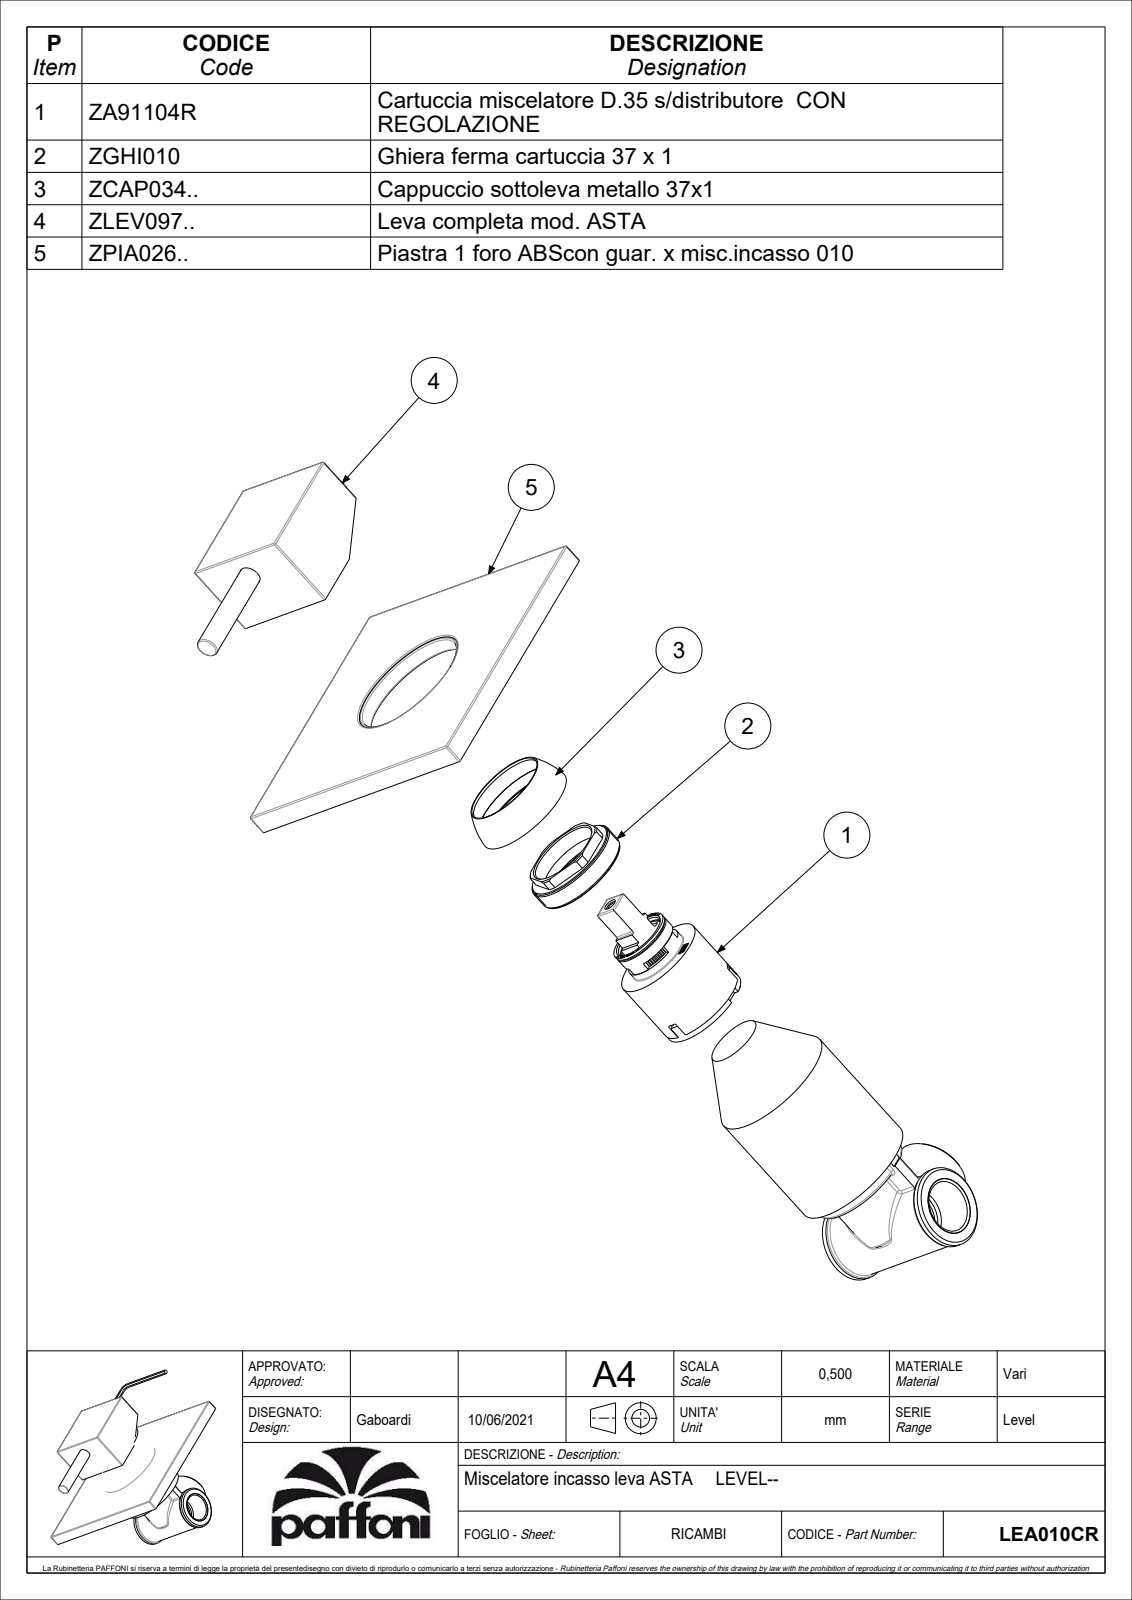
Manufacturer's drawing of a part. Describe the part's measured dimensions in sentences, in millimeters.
The part is named "LEA010CR". Its 3-D file was written by "CREO PARAMETRIC BY PTC INC, 2020044 (CONFIG_CONTROL_DESIGN)". It is 2 solids with 949 faces: 601 planar, 211 cylindrical and 137 other. Overall it measures 117.45 by 110 by 56.1 millimeters. Its volume is 105 290 cubic millimeters and its surface area 68 445 square millimeters. Round holes: 2 of diameter 4, 1 of diameter 3.3, 1 of diameter 5, 1 of diameter 5.5, 1 of diameter 6, 1 of diameter 8.1, 1 of diameter 19.5, 1 of diameter 19.9, 1 of diameter 26.8, 1 of diameter 29, 1 of diameter 31, 1 of diameter 32.4. Round bosses or shafts: 1 of diameter 51, 1 of diameter 49, 1 of diameter 44.8, 1 of diameter 35, 1 of diameter 23.5, 1 of diameter 23.4, 1 of diameter 21.8, 1 of diameter 8. Partial cylindrical surfaces (rounded edges, fillets, slot ends): 37 of radius 0.5, 11 of radius 0.15, 6 of radius 1, 4 of radius 0.3, 4 of radius 2, 1 of radius 7, 1 of radius 9.3, 1 of radius 10.85. The main face-to-face distances are 7, 2, 0.5, 5, 2.5, 108, 50.1, 45, 107.5, 105.5. The hole center spacings are 14.6.
